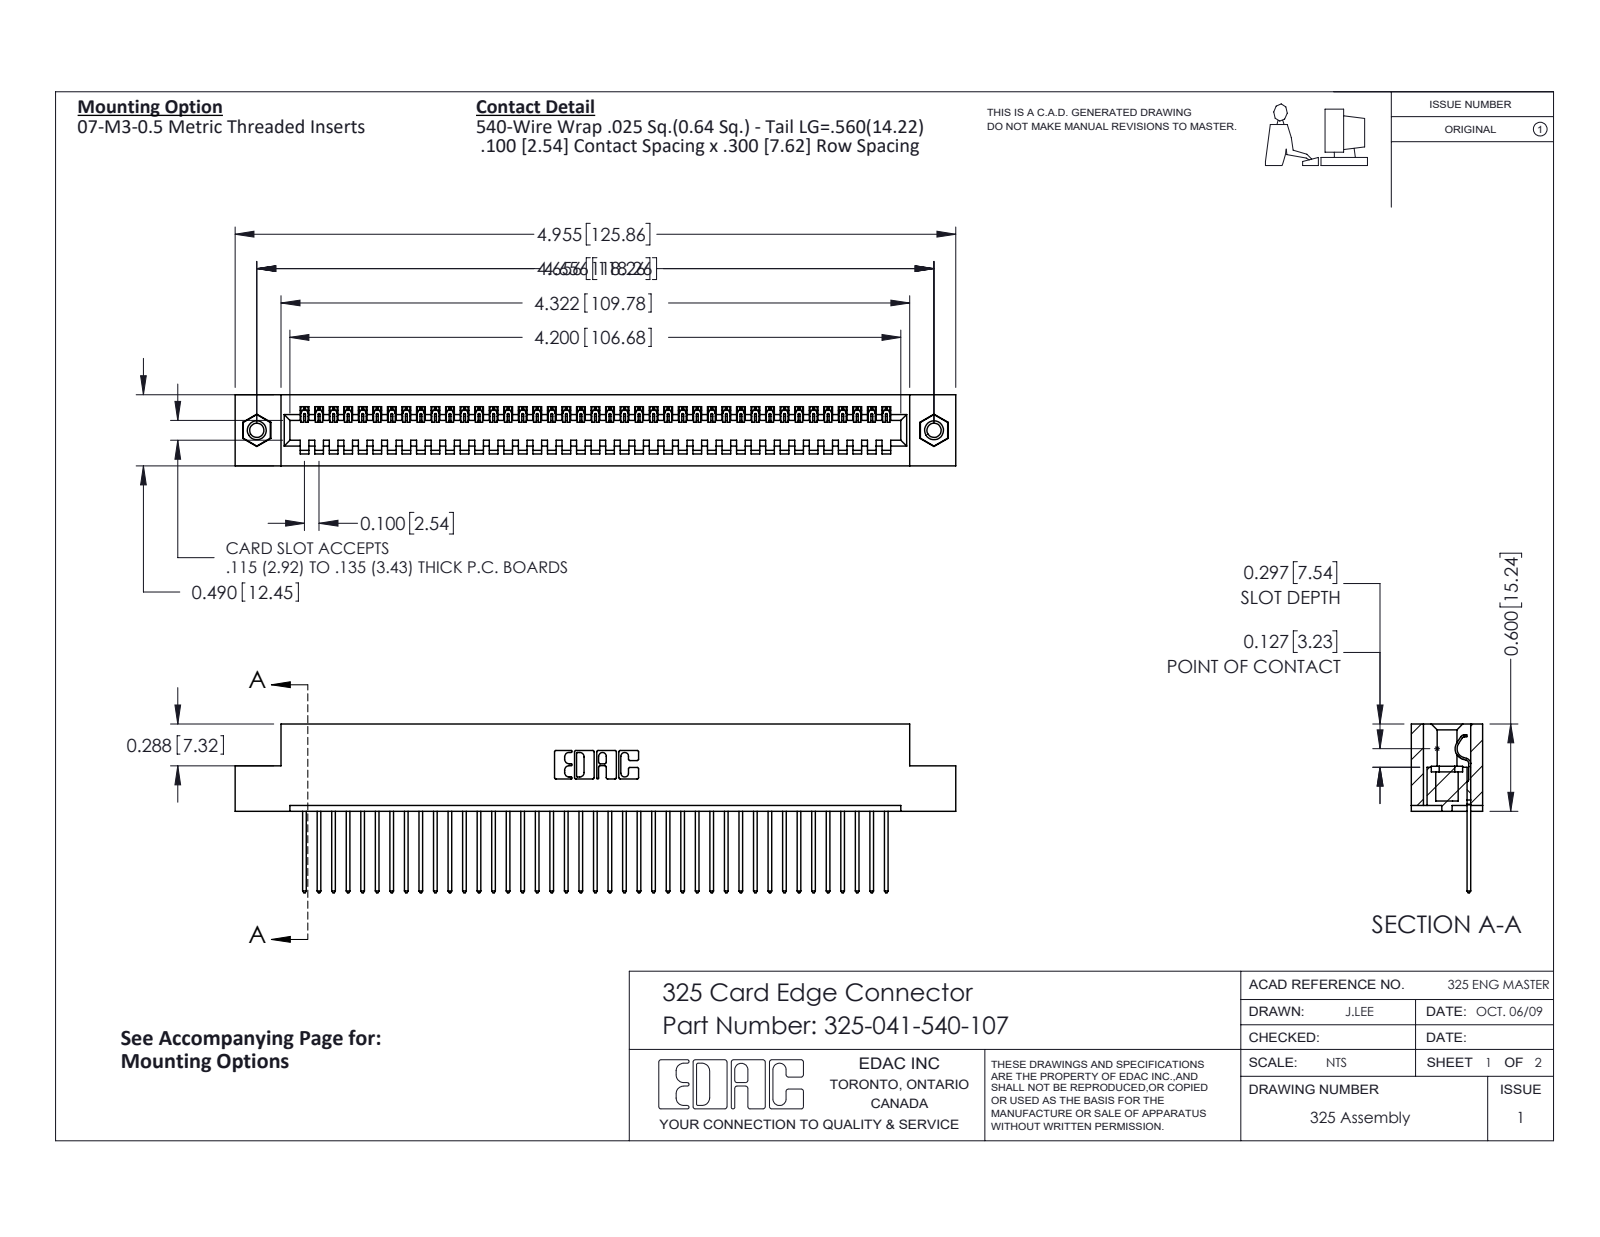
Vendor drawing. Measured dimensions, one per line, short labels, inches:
name: 325-041-540-107; 325-292-001_325-293-140; 345-250-001_345-250-005-103; 325 Part_TI
written by: SolidWorks 2016 (CONFIG_CONTROL_DESIGN)
unit: in
bodies: 44 solids, 2552 faces (1824 planar, 712 cylindrical, 16 other)
size: 4.955 × 1.16 × 0.49
volume: 0.977 in³; area: 27.77 in²
holes: 2× ⌀0.098, 2× ⌀0.125, 2× ⌀0.16
bosses: 2× ⌀0.155
rounds: 82× R0.006, 82× R0.01, 22× R0.01, 6× R0.007, 6× R0.031, 3× R0.026, 1× R0.014, 1× R0.022
face distances: 0.083, 0.407, 0.49, 0.3, 0.107, 0.383, 0.025, 0.325, 0.56, 0.263
hole spacings: 4.656
